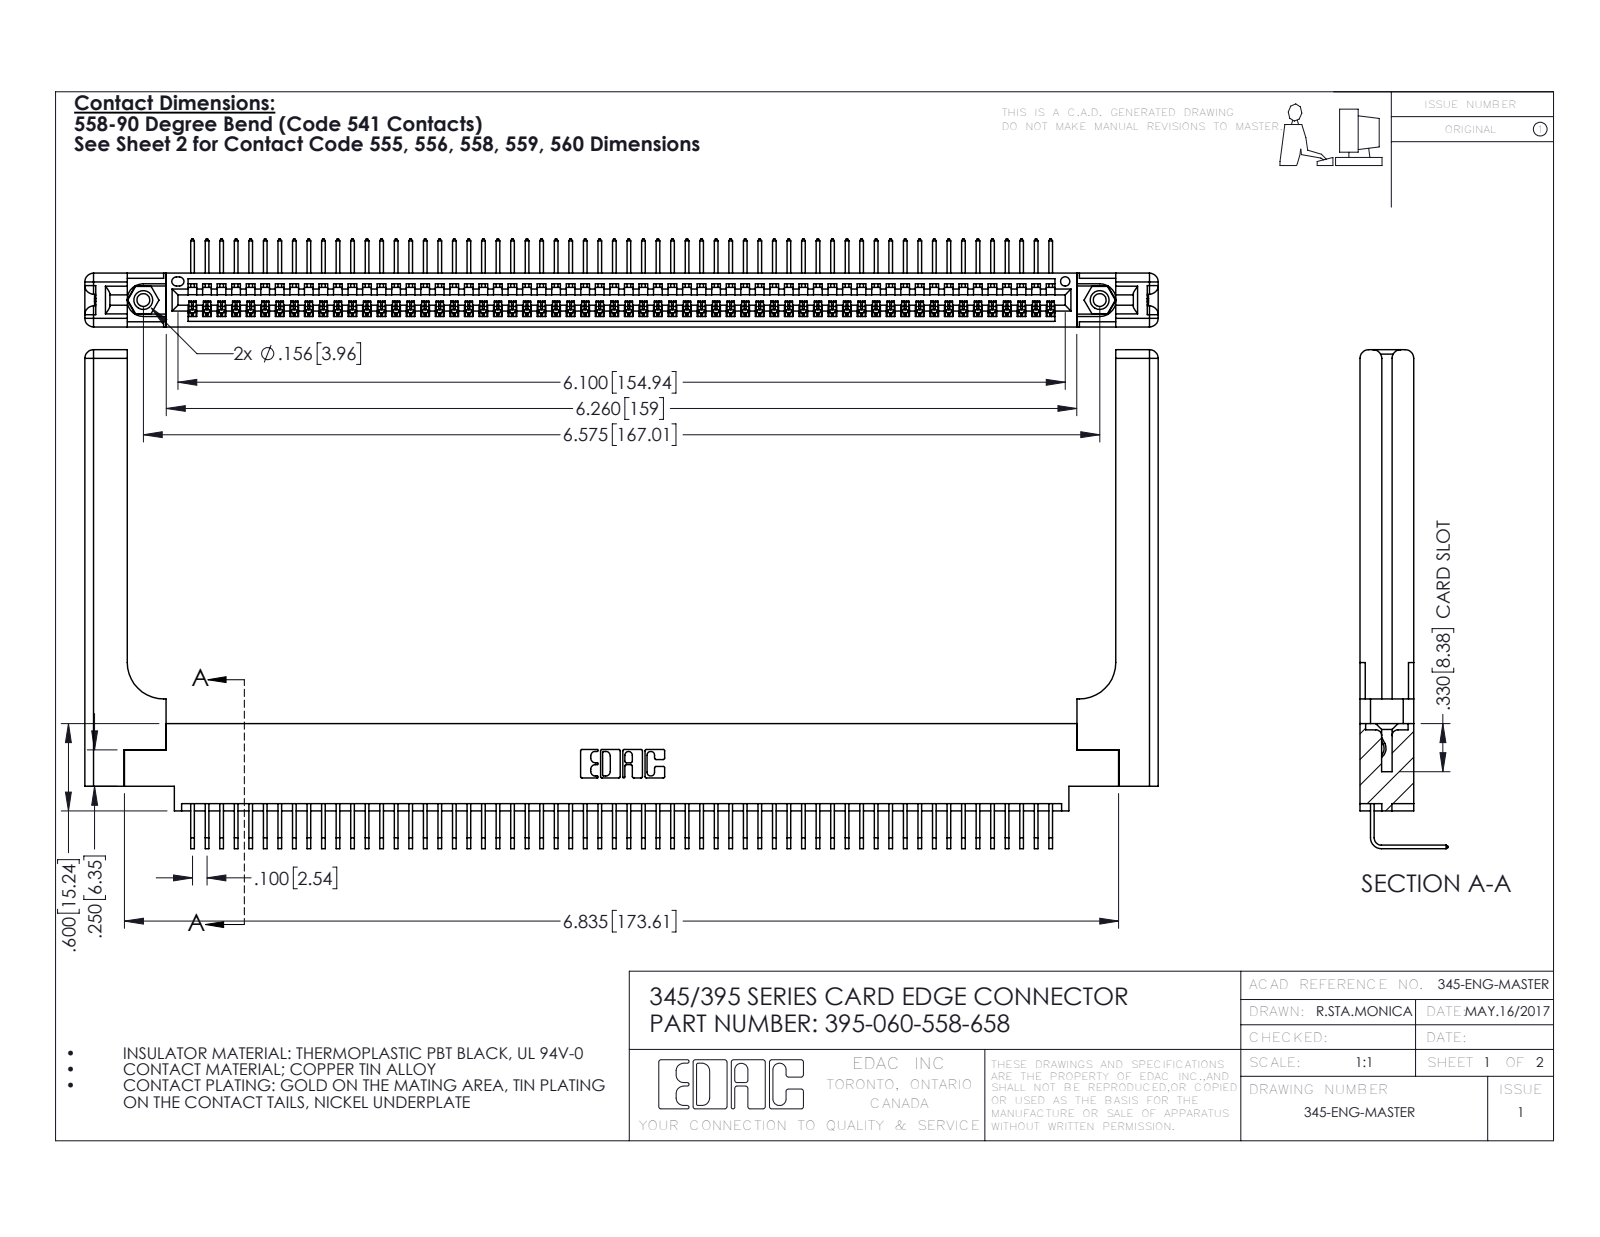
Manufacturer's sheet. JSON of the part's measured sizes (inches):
{"part_name": "345 Part_0.170 Offset - 0.156 Dia-TH; 345-292-001_558 Tail - 2; 395-060-558-658; 345-220-058_345-220-058 (+1 more)", "step_written_by": "SolidWorks 2016 (CONFIG_CONTROL_DESIGN)", "units": "inches", "bodies": {"solids": 65, "faces": 3986, "planar": 2752, "cylindrical": 1174, "other": 60}, "overall_size": [7.379, 3.429, 0.605], "volume_in3": 1.62, "surface_area_in2": 47.77, "round_holes": [[0.089, 2], [0.125, 2], [0.156, 2], [0.064, 1]], "round_bosses_or_shafts": [[0.155, 2]], "partial_cylinders_radius": [[0.006, 120], [0.01, 22], [0.06, 16], [0.007, 6], [0.031, 6], [0.026, 3], [0.03, 2], [0.031, 2]], "face_to_face_distances": [0.072, 0.37, 0.298, 0.098, 0.272, 0.025, 0.2, 0.225, 0.148, 0.15], "hole_center_spacings": [0.27, 6.339, 6.575]}
